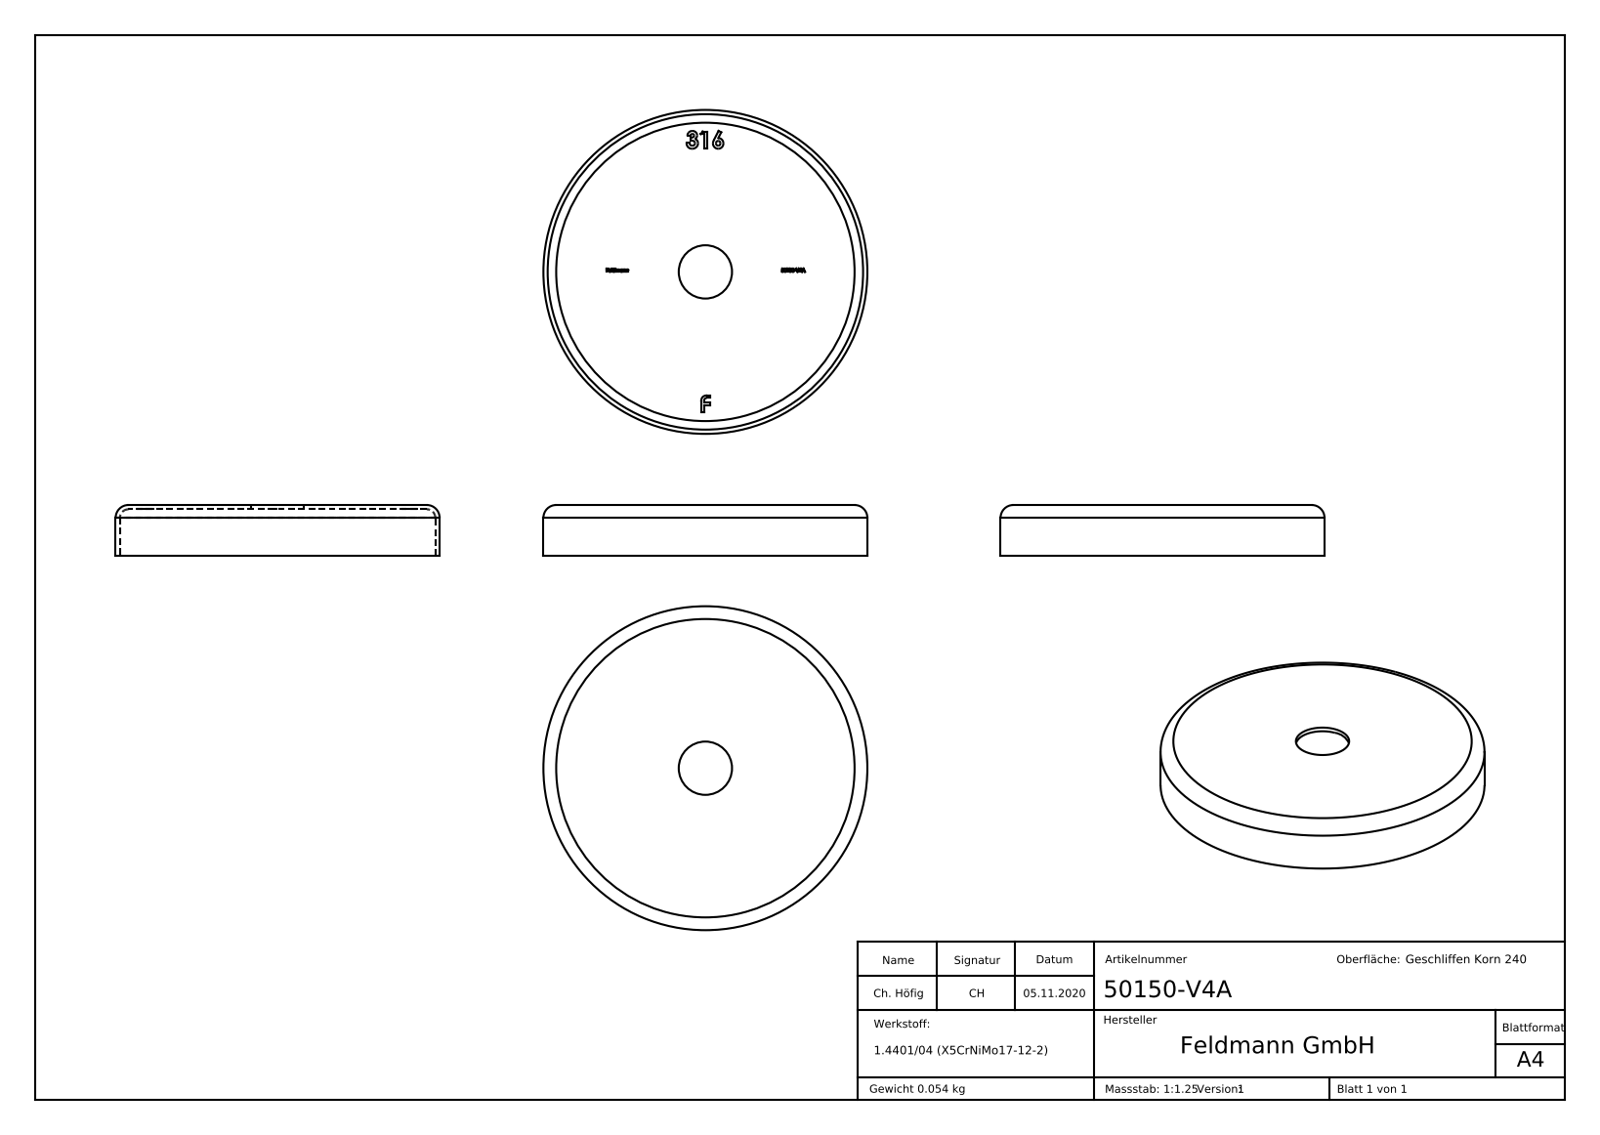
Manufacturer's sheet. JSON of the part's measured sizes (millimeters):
{"part_name": "50150-V4A", "step_written_by": "SolidWorks 2018 (CONFIG_CONTROL_DESIGN)", "units": "millimeters", "bodies": {"solids": 1, "faces": 276, "planar": 161, "cylindrical": 6, "other": 109}, "overall_size": [76, 76, 12], "volume_mm3": 6748, "surface_area_mm2": 13788, "round_holes": [[12.5, 1], [74, 1]], "round_bosses_or_shafts": [[76, 1]], "face_to_face_distances": [1, 11, 12, 11.1, 0.9, 0.71, 0.75, 0.73, 1.44, 0.68]}
